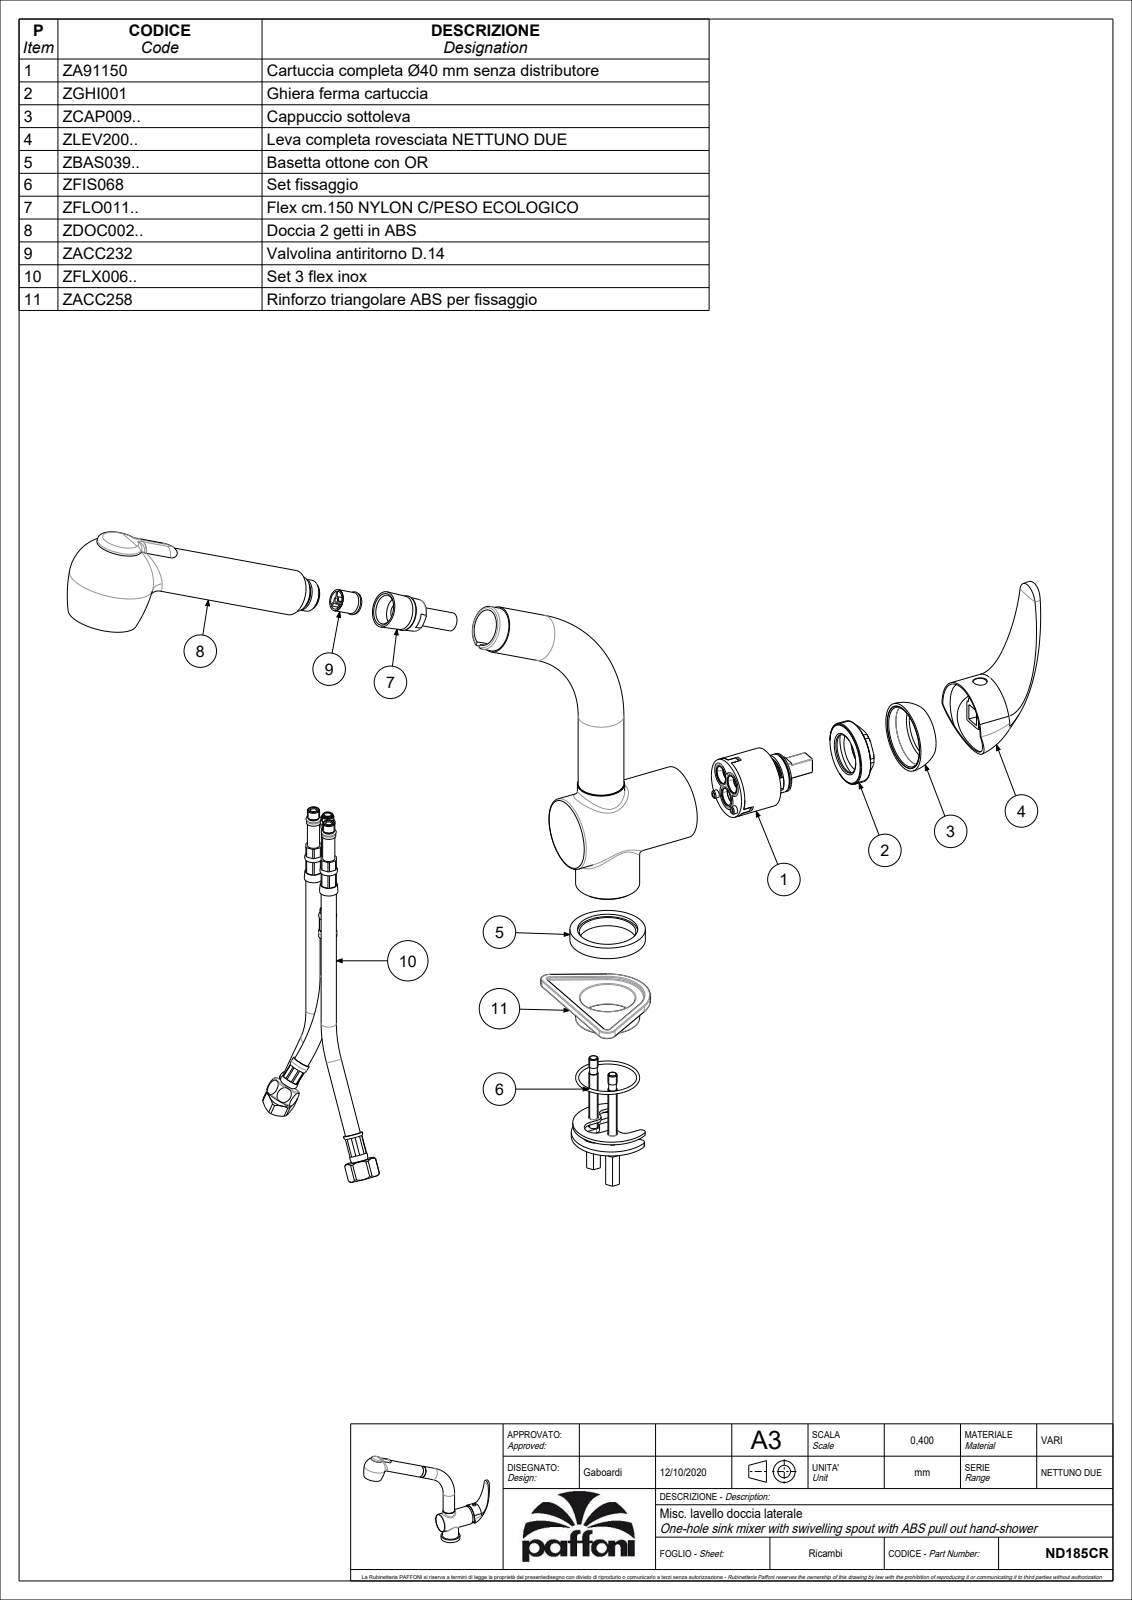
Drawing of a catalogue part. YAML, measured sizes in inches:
part_name: "ND185CR"
step_written_by: "CREO PARAMETRIC BY PTC INC, 2020044 (CONFIG_CONTROL_DESIGN)"
units: inches
bodies: {solids: 2, faces: 338, planar: 95, cylindrical: 101, other: 142}
overall_size: [14.641, 12.159, 2.205]
volume: 27.63
surface_area: 186.4
round_holes:
  - {diameter: 0.276, count: 5}
  - {diameter: 0.339, count: 3}
  - {diameter: 0.37, count: 3}
  - {diameter: 0.207, count: 2}
  - {diameter: 0.217, count: 2}
  - {diameter: 0.63, count: 2}
  - {diameter: 0.945, count: 2}
  - {diameter: 0.236, count: 1}
  - {diameter: 0.315, count: 1}
  - {diameter: 0.906, count: 1}
  - {diameter: 1.012, count: 1}
  - {diameter: 1.031, count: 1}
round_bosses_or_shafts:
  - {diameter: 1.181, count: 2}
  - {diameter: 0.197, count: 2}
  - {diameter: 1.949, count: 1}
  - {diameter: 1.89, count: 1}
  - {diameter: 1.654, count: 1}
  - {diameter: 1.524, count: 1}
  - {diameter: 1.22, count: 1}
  - {diameter: 1.173, count: 1}
partial_cylinders:
  - {radius: 0.315, count: 2}
  - {radius: 0.079, count: 1}
  - {radius: 0.154, count: 1}
  - {radius: 0.157, count: 1}
  - {radius: 0.472, count: 1}
  - {radius: 0.591, count: 1}
  - {radius: 1.969, count: 1}
face_to_face_distances: [1.337, 1.909, 0.572, 0.315, 0.268, 0.267, 0.314, 0.047, 0.118, 2.204]
hole_center_spacings: [0.44, 0.463, 0.483, 0.496, 0.504, 0.511, 0.615, 0.646]
